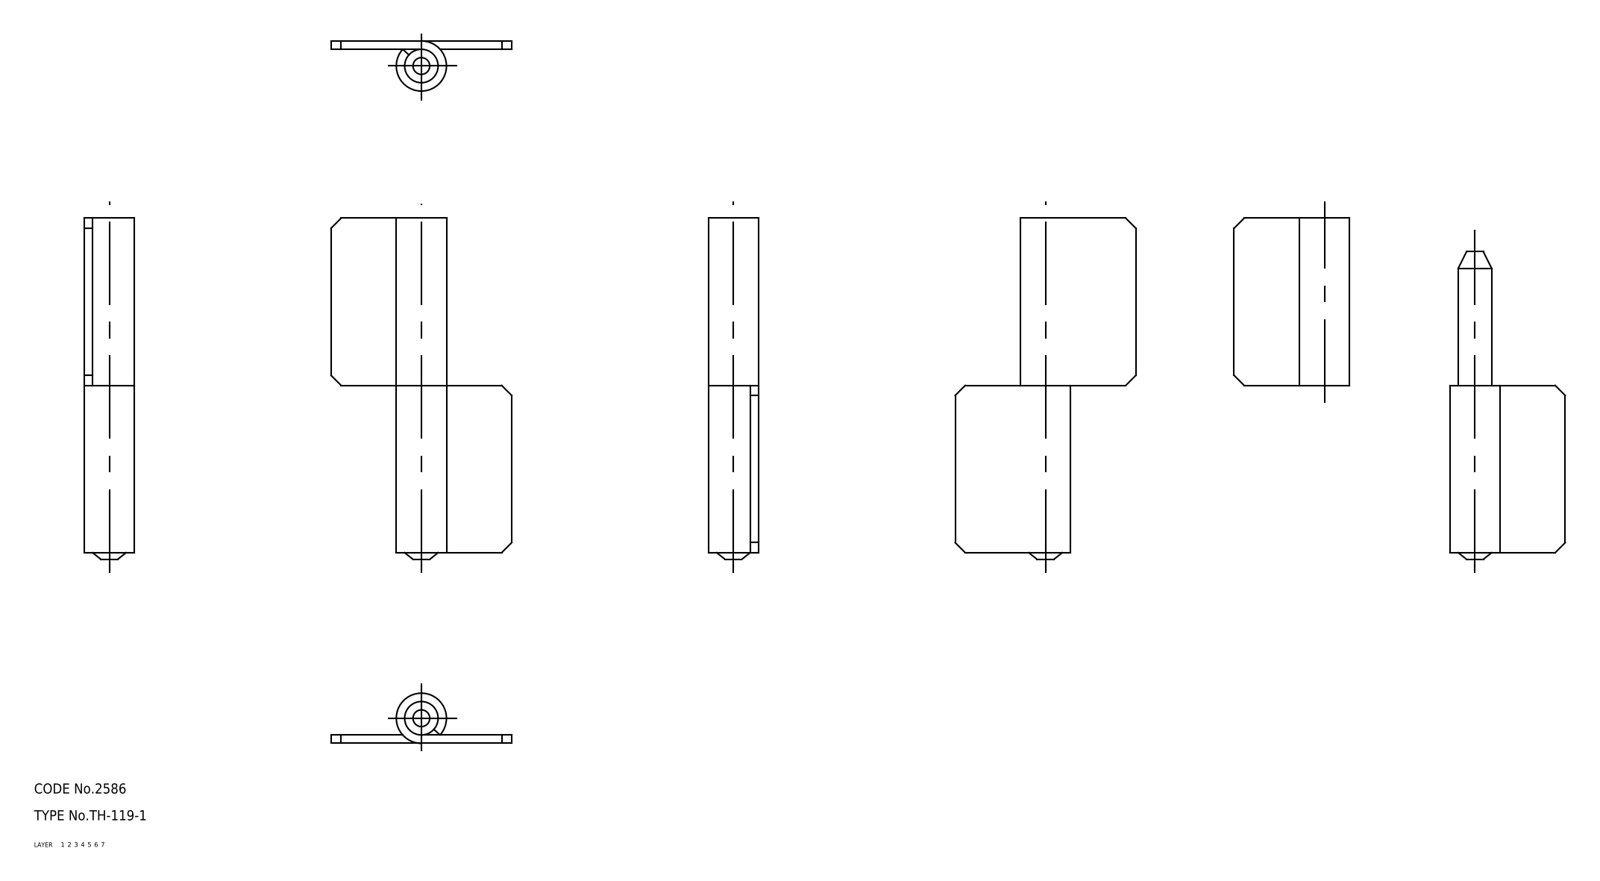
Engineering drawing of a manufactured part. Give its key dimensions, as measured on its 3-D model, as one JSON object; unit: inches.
{"part_name": "shaft; hinge piece_B; hinge piece_A; TH_119_1_32735_36", "step_written_by": "CADfix (AUTOMOTIVE_DESIGN)", "units": "inches", "bodies": {"solids": 3, "faces": 28, "planar": 0, "cylindrical": 0, "other": 28}, "overall_size": [4.016, 2.126, 0.591], "volume_in3": 1.355, "surface_area_in2": 25.06}
